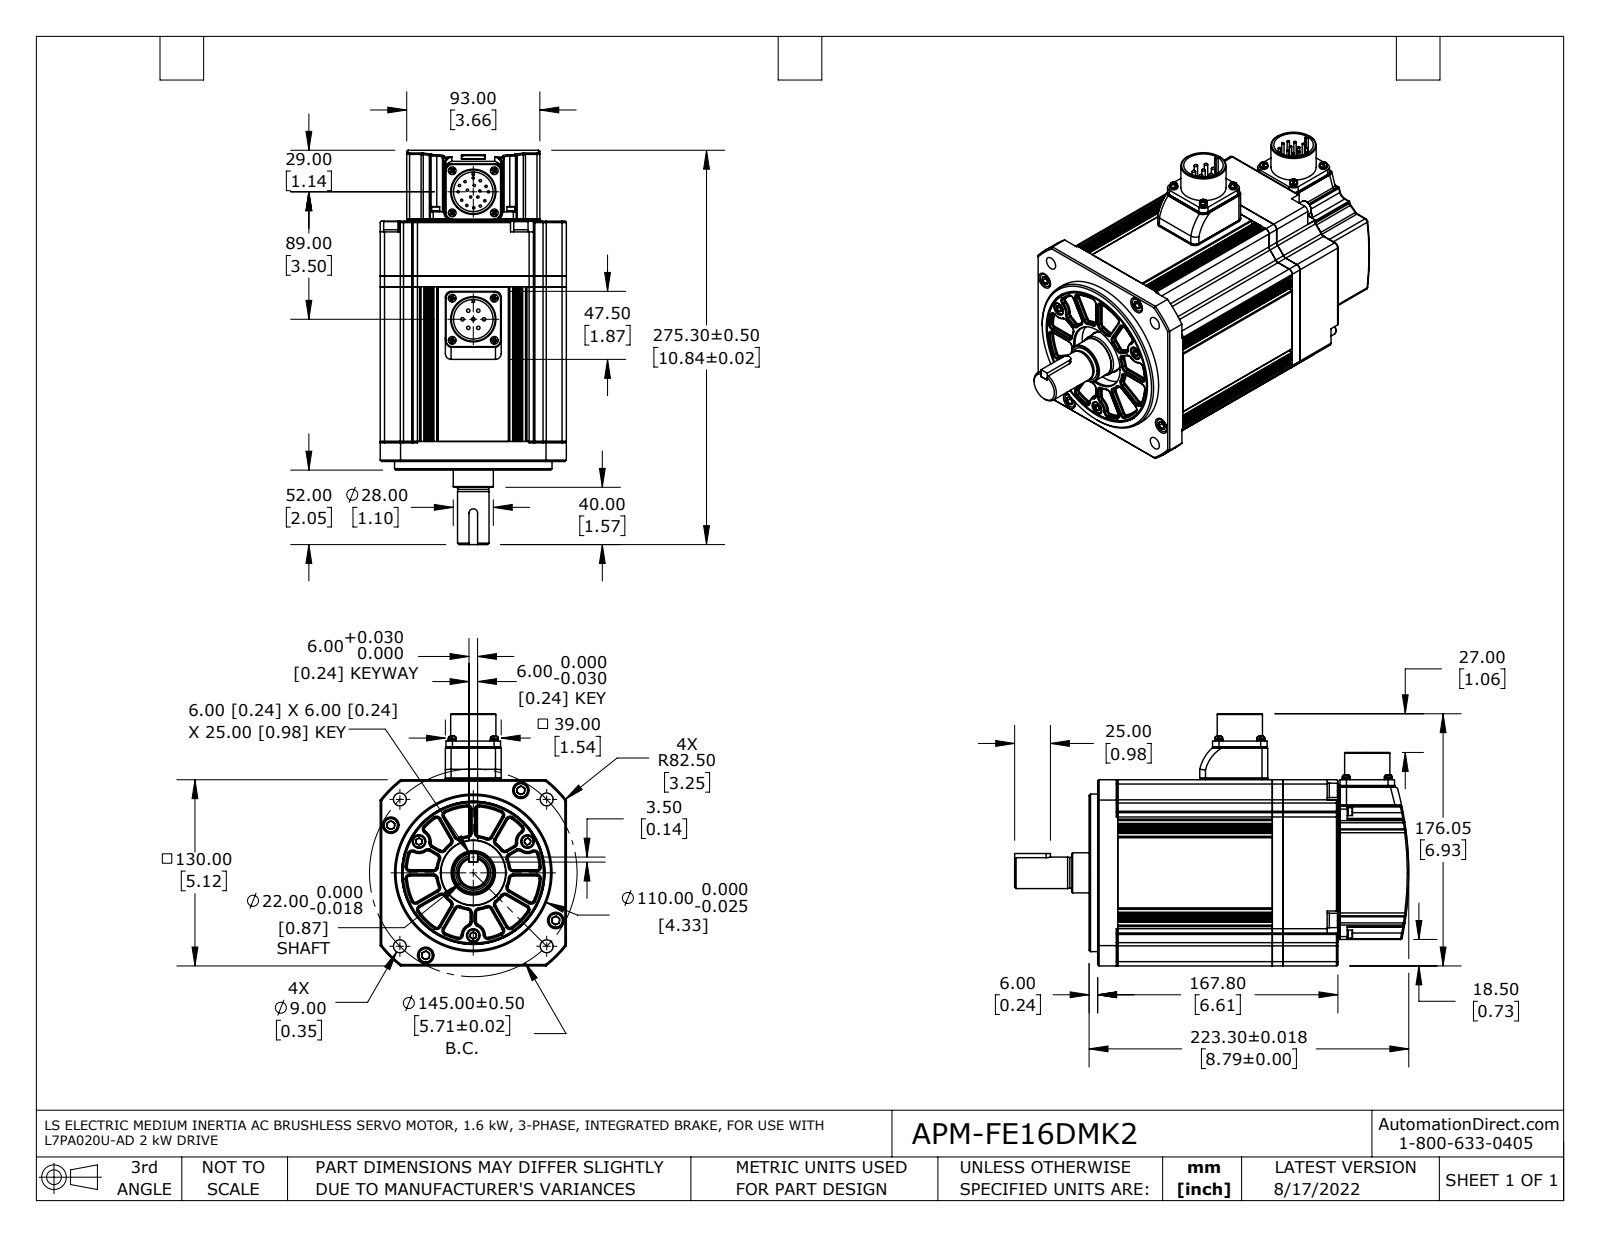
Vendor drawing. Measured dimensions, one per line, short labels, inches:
name: FM13GA003G03_Out Line(APM-FE16D_K2) r1 nc fxt
written by: SolidWorks 2017 (AUTOMOTIVE_DESIGN)
unit: in
bodies: 57 solids, 2214 faces (729 planar, 843 cylindrical, 642 other)
size: 10.839 × 6.931 × 5.118
volume: 182.5 in³; area: 550.4 in²
holes: 12× ⌀0.098, 8× ⌀0.118, 8× ⌀0.12, 8× ⌀0.138, 7× ⌀0.197, 4× ⌀0.142, 4× ⌀0.146, 4× ⌀0.268, 4× ⌀0.276, 4× ⌀0.354, 4× ⌀0.453, 3× ⌀0.22
bosses: 17× ⌀0.063, 8× ⌀0.213, 7× ⌀0.094, 4× ⌀0.402, 4× ⌀0.394, 4× ⌀0.236, 4× ⌀0.217, 4× ⌀0.118
rounds: 72× R0.02, 54× R0.098, 24× R0.028, 22× R0.039, 17× R0.079, 17× R0.118, 12× R0.177, 8× R0.157
face distances: 4.252, 0.299, 4.551, 0.039, 5.118, 6.114, 0.906, 1.524, 1.823, 6.075
hole spacings: 0.819, 1.157, 3.504, 0.752, 1.041, 1.637, 1.975, 2.618
